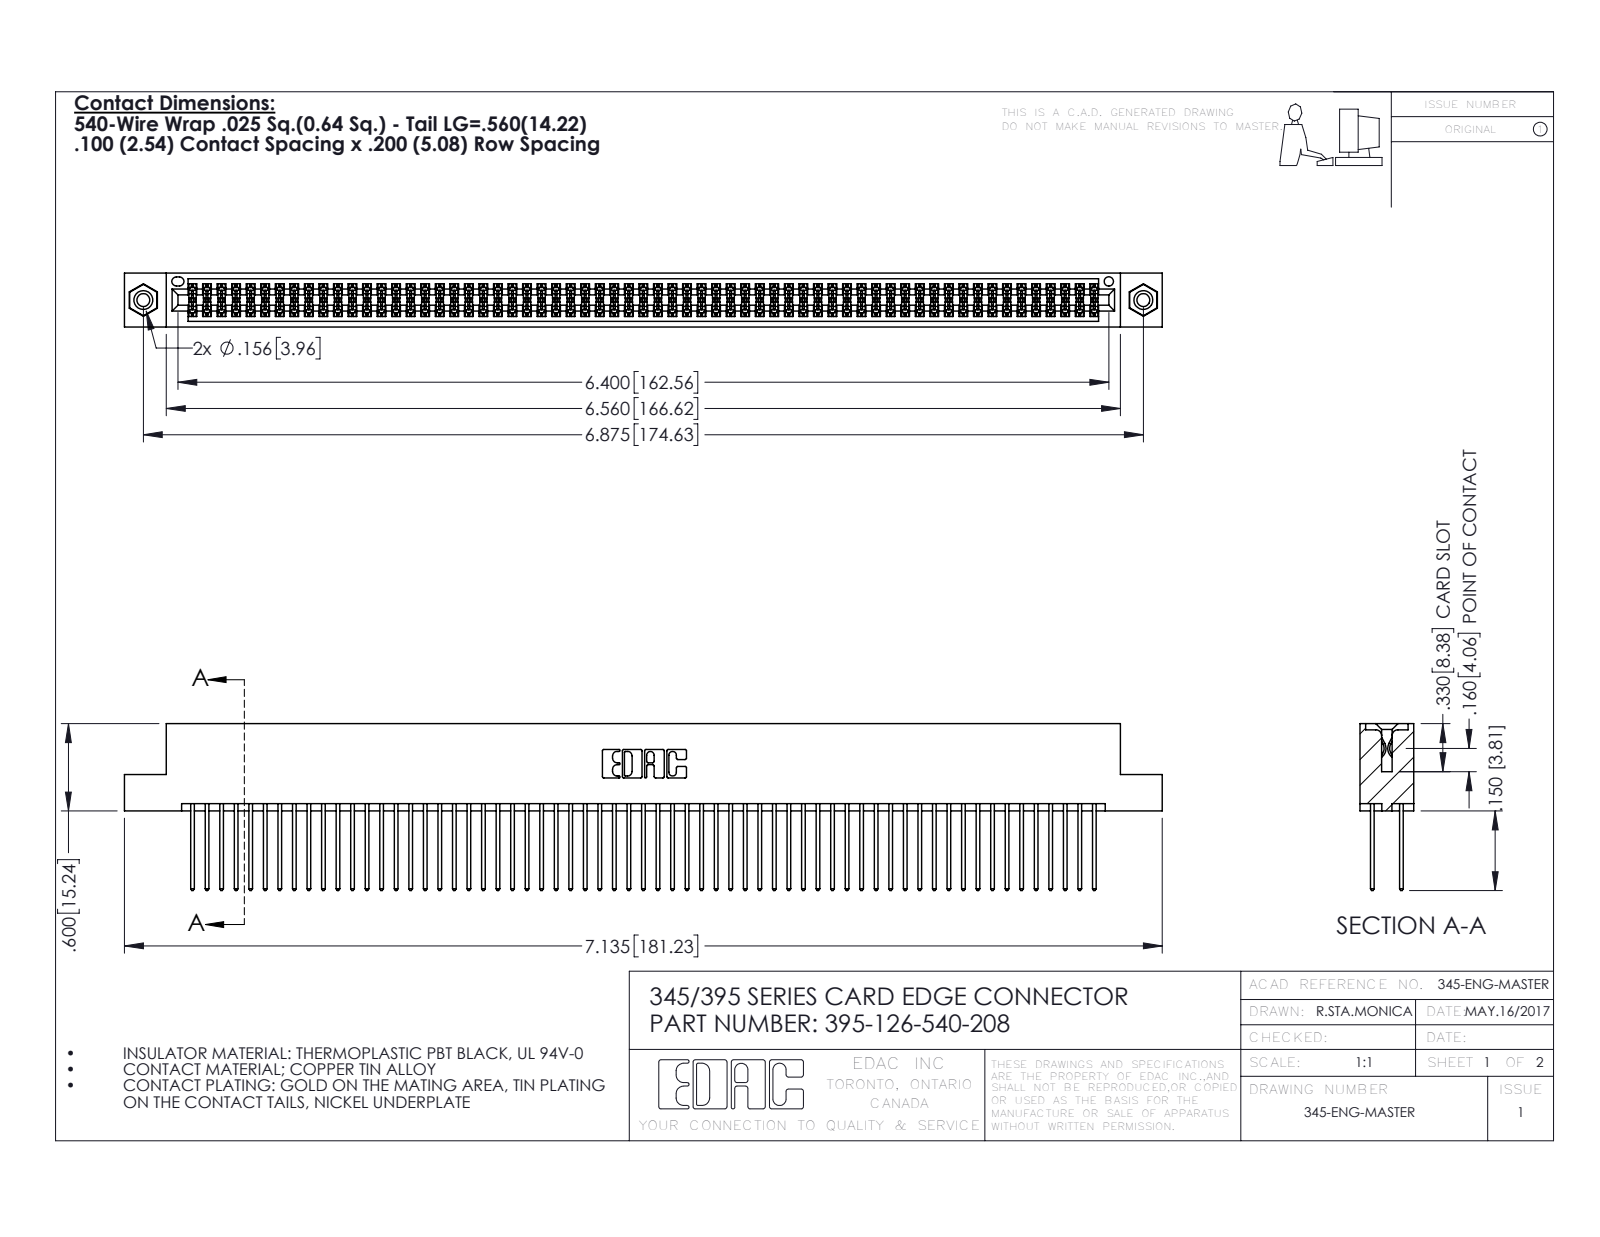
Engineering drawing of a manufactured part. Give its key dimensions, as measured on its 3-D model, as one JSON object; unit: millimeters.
{"part_name": "345 Part_Flush Mounting Lugs - 0.156 Dia-TI; 395-126-540-208; 345-292-001_345-293-140; 345-250-001_345-250-003-102", "step_written_by": "SolidWorks 2016 (CONFIG_CONTROL_DESIGN)", "units": "millimeters", "bodies": {"solids": 129, "faces": 6486, "planar": 4270, "cylindrical": 2200, "other": 16}, "overall_size": [181.2, 29.1, 9.4], "volume_mm3": 18270, "surface_area_mm2": 29650, "round_holes": [[2.3, 2], [3.2, 2], [4, 2], [1.6, 1]], "round_bosses_or_shafts": [[3.9, 2]], "partial_cylinders_radius": [[0.2, 189], [0.3, 126], [0.3, 22], [0.2, 6], [0.8, 6], [0.7, 3], [0.4, 2], [0.5, 2]], "face_to_face_distances": [1.8, 7.6, 5.1, 2.5, 6.9, 0.6, 9.4, 5.7, 4.4, 3.8], "hole_center_spacings": [6.9, 168.6, 174.6]}
